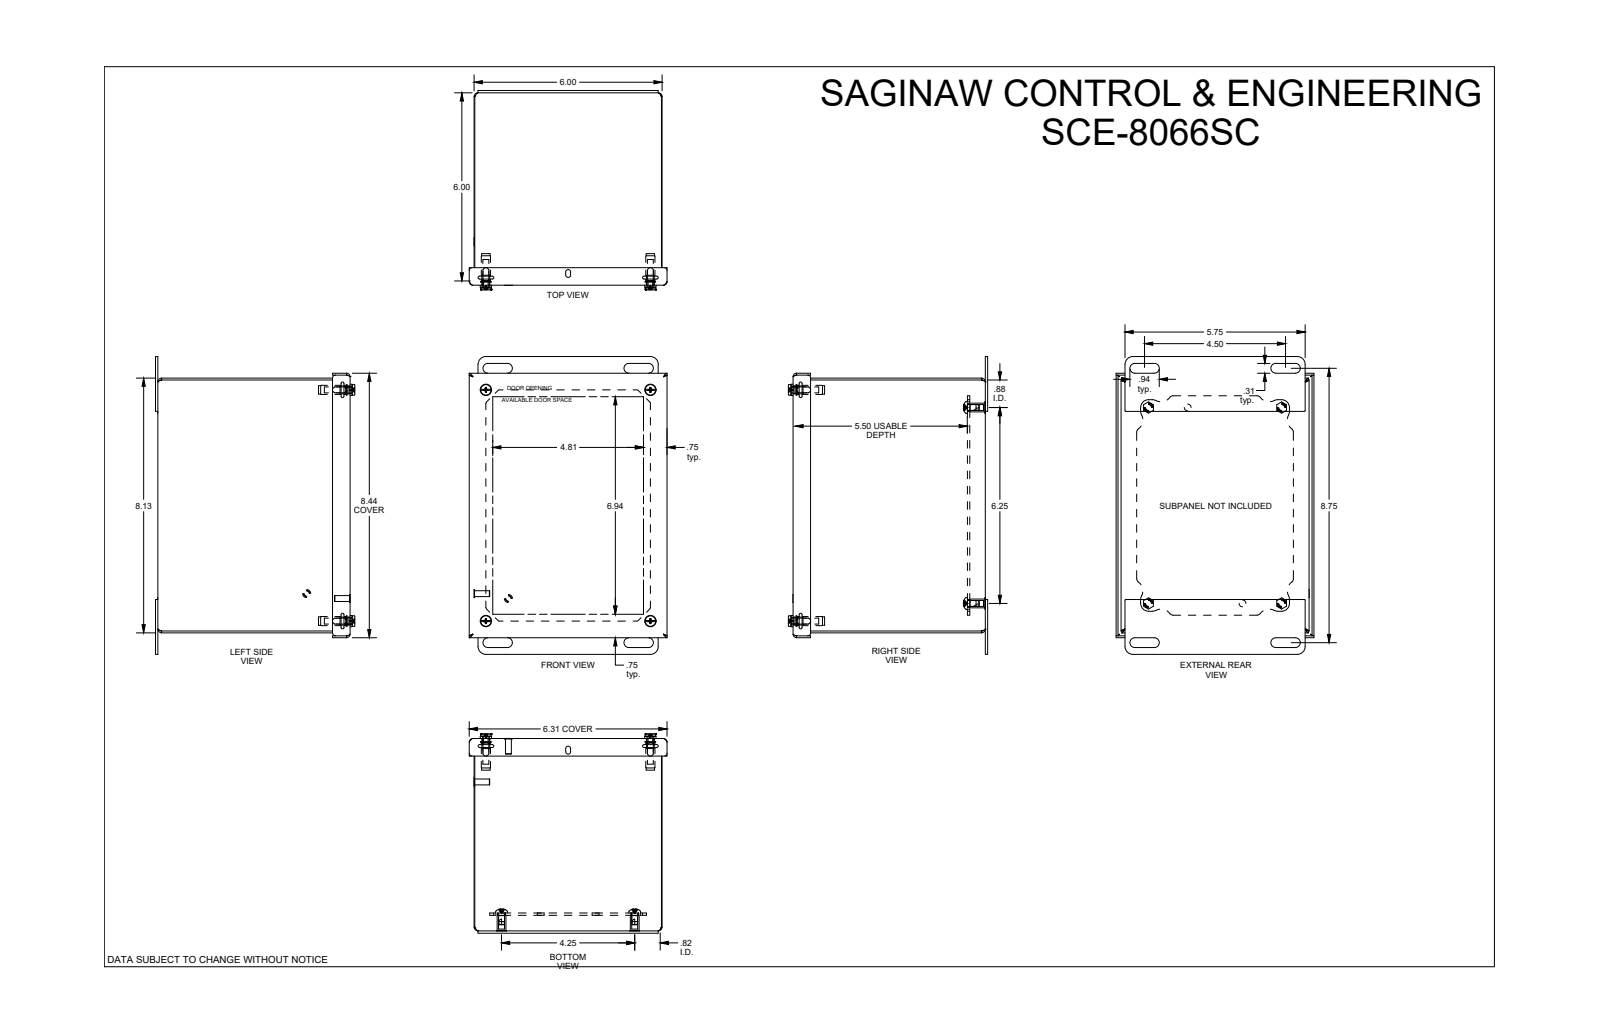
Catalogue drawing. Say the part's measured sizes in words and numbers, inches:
The part is named "SCE-8066SC". Its 3-D file was written by "SolidWorks 2019 (CONFIG_CONTROL_DESIGN)". It is 0 solids with 879 faces: 397 planar, 216 cylindrical and 266 other. Overall it measures 9.5 by 6.361 by 6.313 inches. Round holes: 8 of diameter 0.19, 8 of diameter 0.25, 4 of diameter 0.22, 4 of diameter 0.266, 4 of diameter 0.281, 4 of diameter 0.317, 2 of diameter 0.193, 2 of diameter 0.218. Round bosses or shafts: 10 of diameter 0.188, 4 of diameter 0.373, 4 of diameter 0.362, 4 of diameter 0.34, 4 of diameter 0.334, 4 of diameter 0.292, 4 of diameter 0.28, 4 of diameter 0.27. Partial cylindrical surfaces (rounded edges, fillets, slot ends): 16 of radius 0.125, 16 of radius 0.25, 8 of radius 0.005, 8 of radius 0.007, 8 of radius 0.052, 8 of radius 0.112, 8 of radius 0.156, 8 of radius 0.255. The main face-to-face distances are 0.06, 5.94, 6.075, 6, 5.88, 6.135, 6.015, 0.06, 5.505, 0.075. The hole center spacings are 0.753, 8.305, 6.831, 4.783, 5.25, 5.25, 7.375, 7.375.
